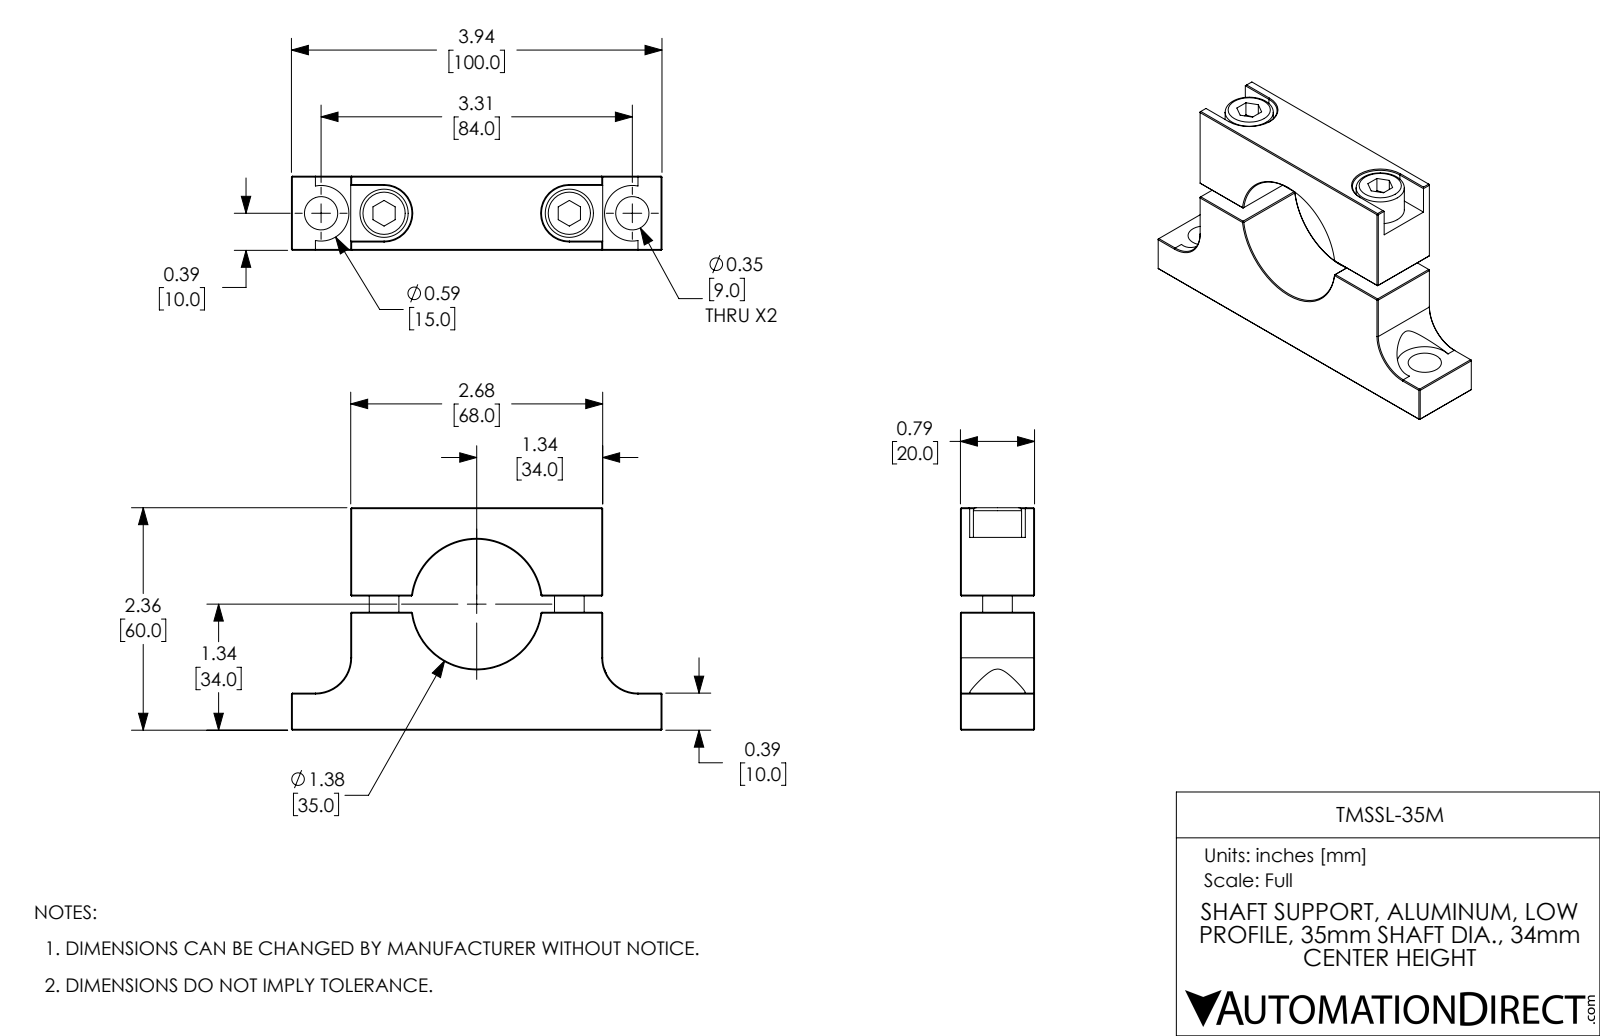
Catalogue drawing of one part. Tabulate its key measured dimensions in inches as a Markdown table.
| quantity | value |
| --- | --- |
| part name | TMSSL-35M |
| STEP written by | SolidWorks 2017 (AUTOMOTIVE_DESIGN) |
| units | inches |
| bodies | 4 solids, 179 faces (118 planar, 32 cylindrical, 29 other) |
| overall size | 3.937 × 2.362 × 0.787 |
| volume | 3.787 in³ |
| surface area | 33.16 in² |
| round holes (diameter × count) | 0.354 × 4, 0.262 × 2, 0.094 × 1, 1.378 × 1 |
| round bosses / shafts (diameter × count) | 0.512 × 2, 0.315 × 2 |
| partial cylindrical surfaces (radius × count) | 0.296 × 4, 0.375 × 2 |
| main face-to-face distances | 0.787, 2.362, 2.677, 1.252, 1.11, 1.425, 0.172, 0.937, 2.047, 0.795 |
| hole center spacings | 0.669, 0.984, 1.654, 2.638, 1.969, 3.307 |
